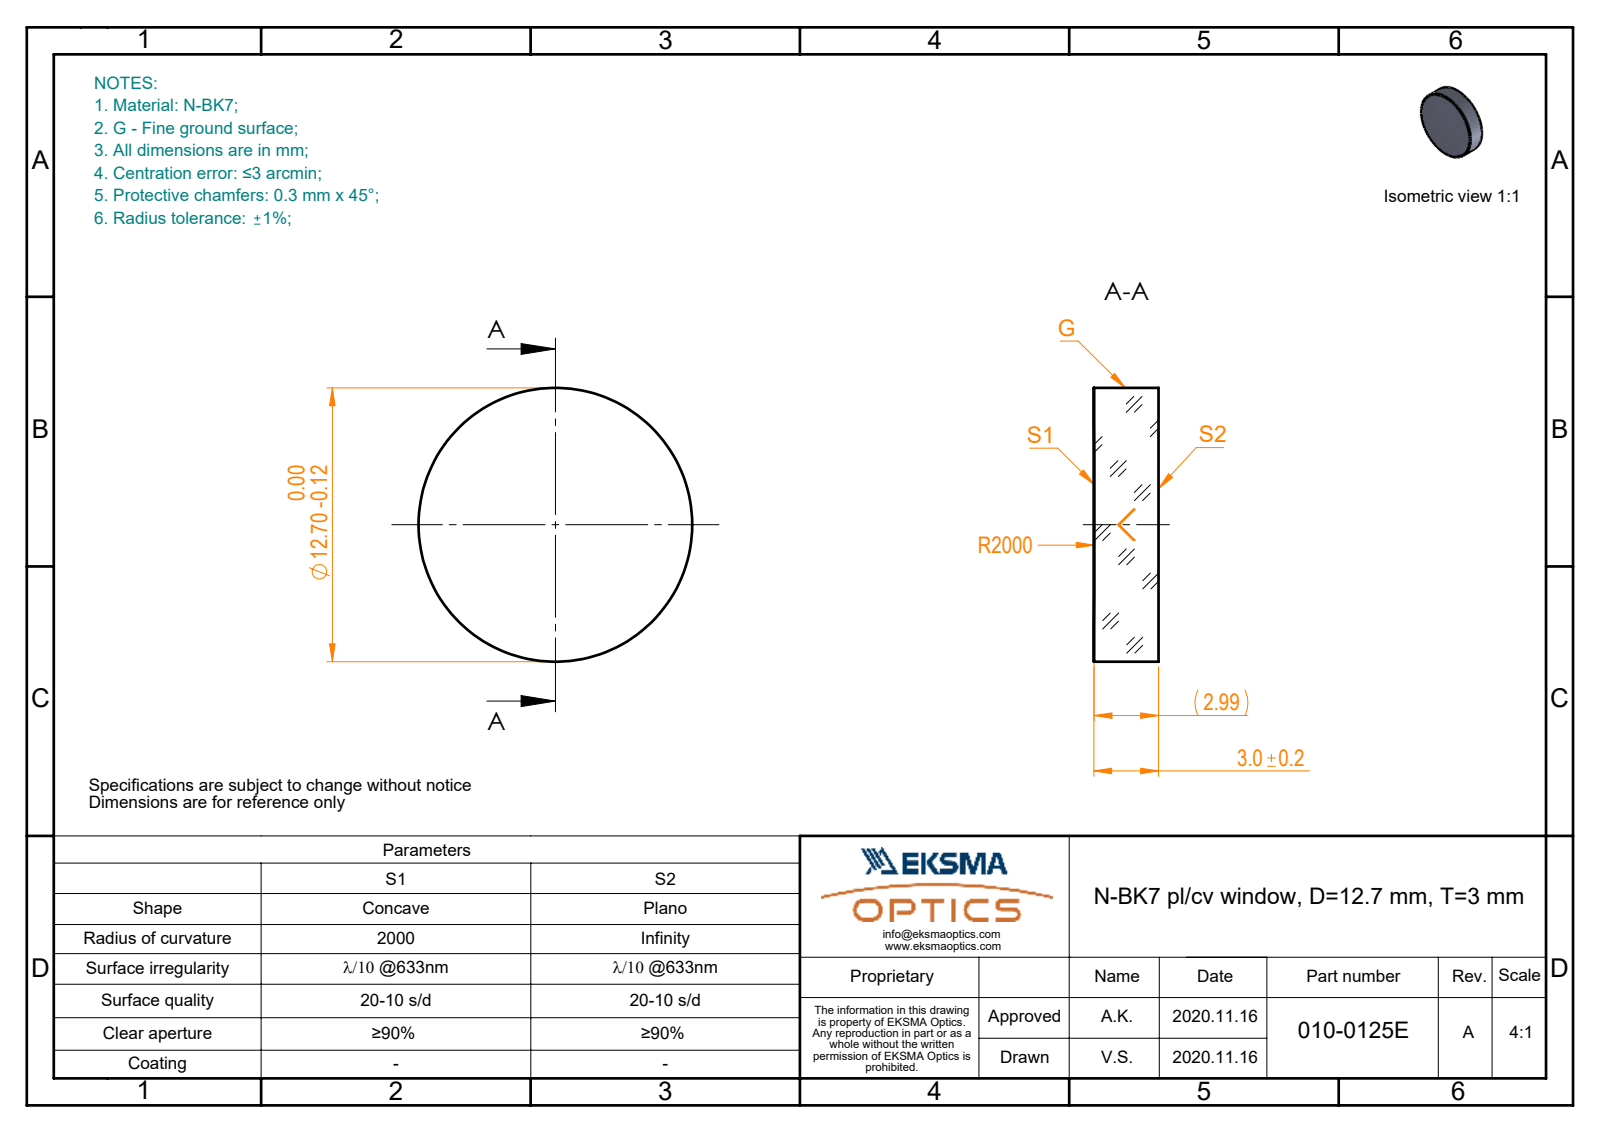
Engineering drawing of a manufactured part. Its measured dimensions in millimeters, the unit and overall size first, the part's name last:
Units: millimetres
Overall size (bounding box): 12.7 × 12.7 × 3
Round bosses / shafts (diameter × count): ⌀12.7 ×1
Volume: 379 mm³ · Surface area: 373 mm²
Bodies: 1 solid, 5 faces (1 planar, 2 cylindrical, 2 other)
Part name (STEP PRODUCT): 010-0125E_N-BK7_PCV_window
STEP written by: SolidWorks 2019 (CONFIG_CONTROL_DESIGN)
